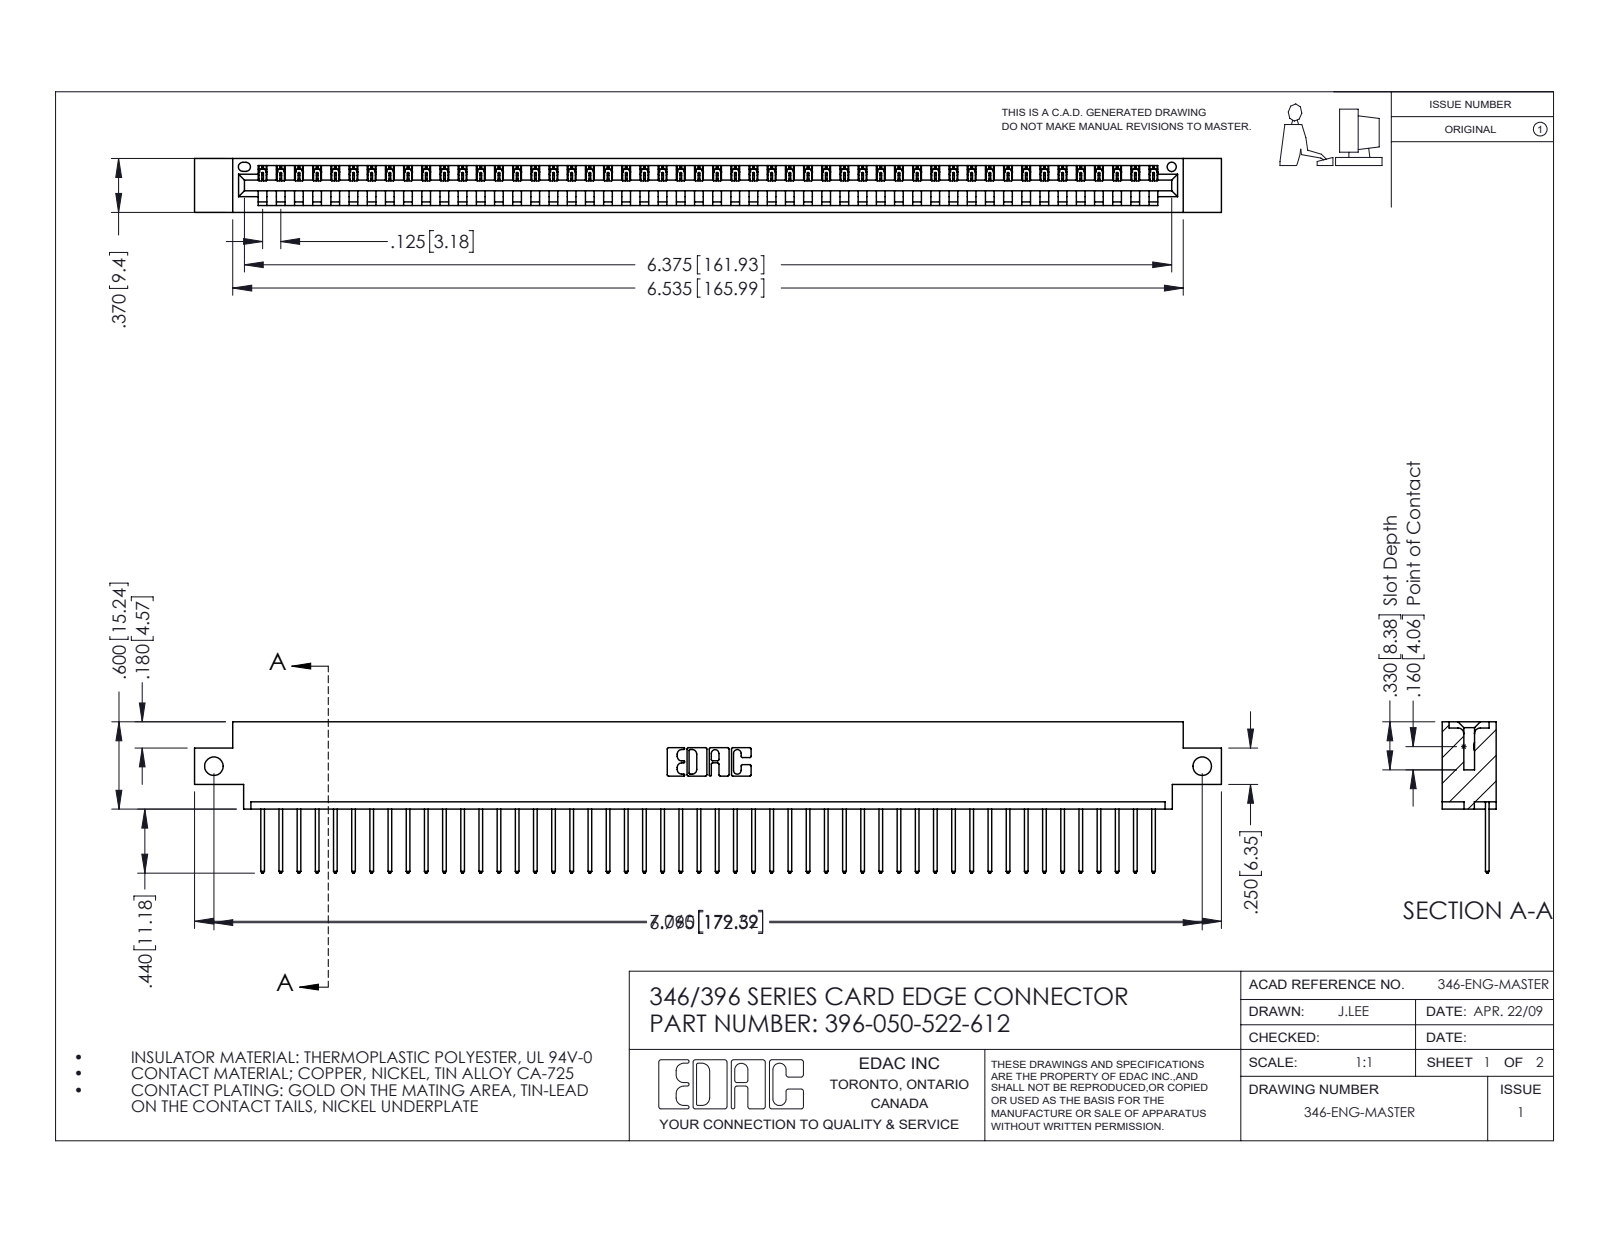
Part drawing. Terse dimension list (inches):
name: 345-292-001_345-293-122; 346 Part_0.170 Offset - Side Mount; 396-050-522-612
written by: SolidWorks 2016 (CONFIG_CONTROL_DESIGN)
unit: in
bodies: 51 solids, 3026 faces (2080 planar, 946 cylindrical, 0 other)
size: 7.06 × 1.04 × 0.37
volume: 1.036 in³; area: 33.35 in²
holes: 2× ⌀0.128, 1× ⌀0.064
rounds: 100× R0.006, 100× R0.01, 22× R0.01, 6× R0.007, 6× R0.031, 3× R0.026, 2× R0.031, 2× R0.04
face distances: 0.048, 0.322, 0.37, 0.25, 0.072, 0.298, 0.025, 0.148, 0.222, 0.1
hole spacings: 6.795
